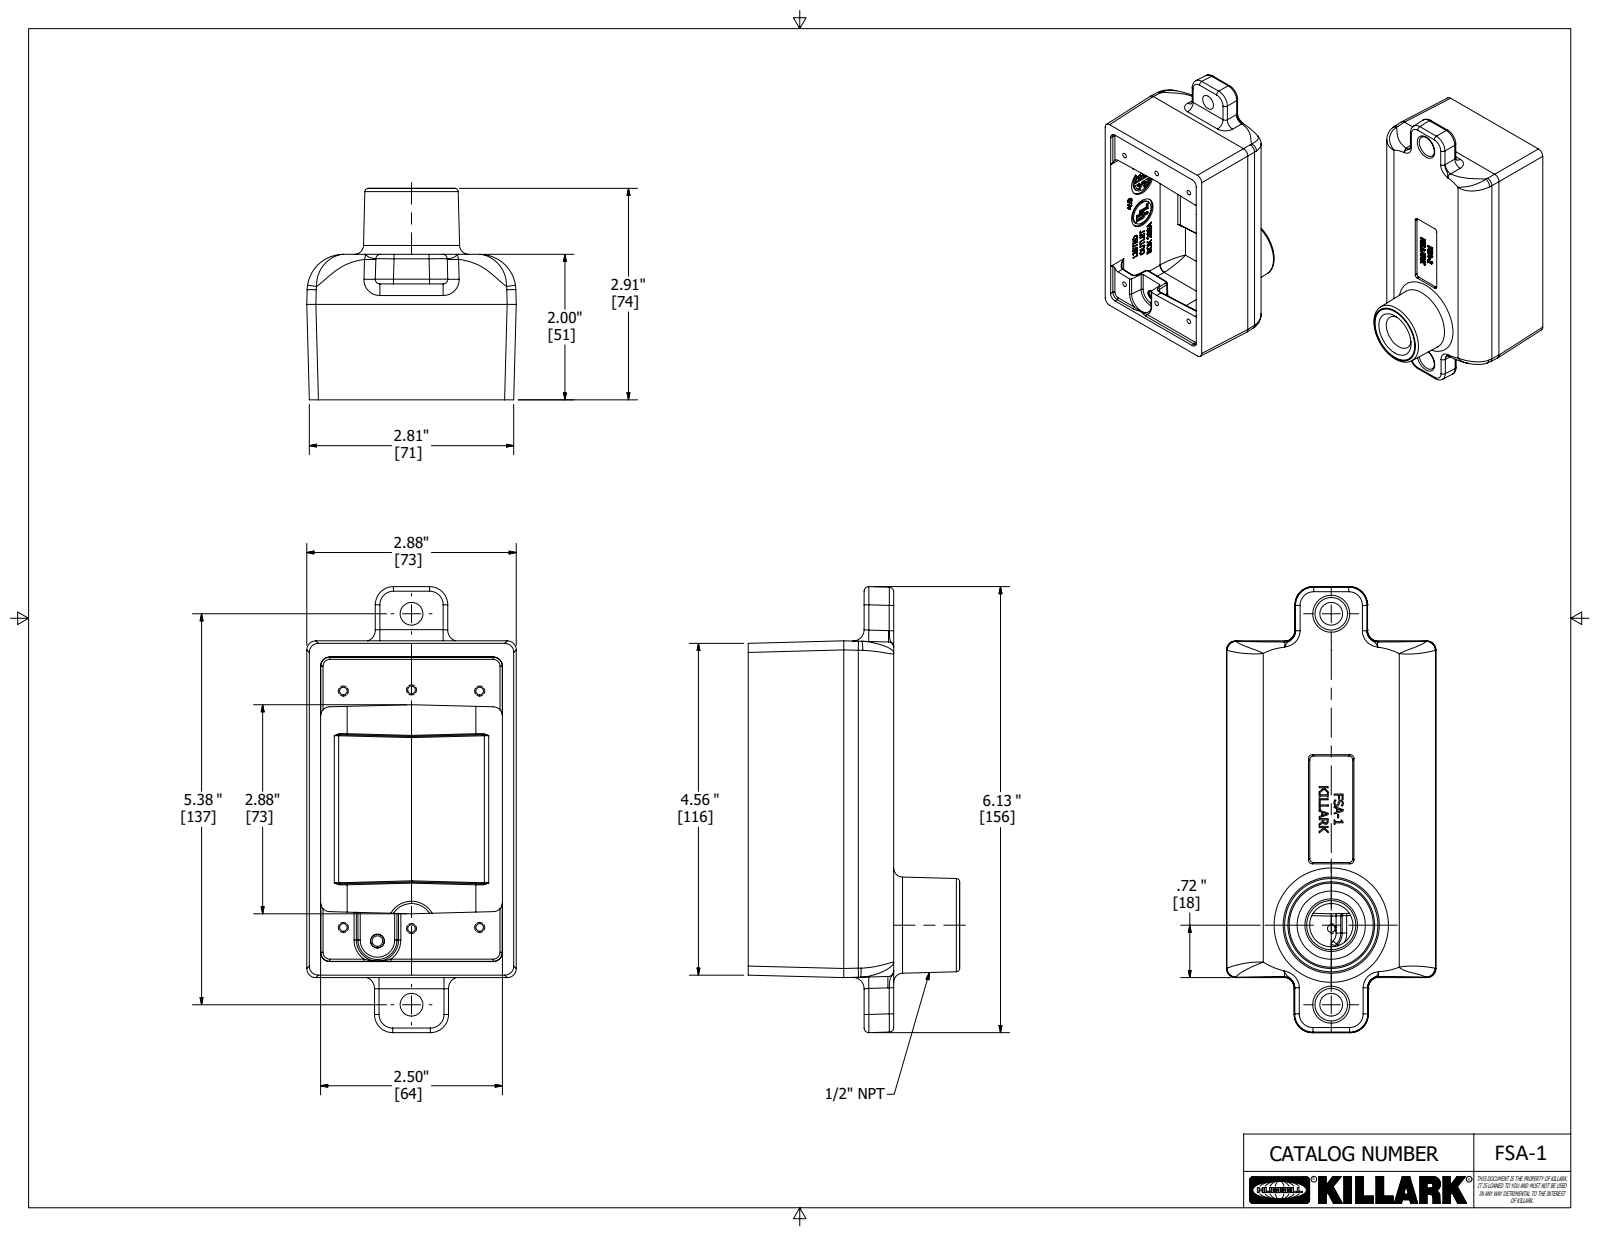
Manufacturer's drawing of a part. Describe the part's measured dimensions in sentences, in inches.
The part is named "24225-2". Its 3-D file was written by "Autodesk Inventor 2020 (AUTOMOTIVE_DESIGN)". It is 1 solid with 1111 faces: 585 planar, 130 cylindrical and 396 other. Overall it measures 6.132 by 2.908 by 2.881 inches. Its volume is 8.961 cubic inches and its surface area 91.74 square inches. Round holes: 6 of diameter 0.104, 1 of diameter 0.069, 1 of diameter 0.145, 1 of diameter 0.595, 1 of diameter 0.625. Round bosses or shafts: 1 of diameter 0.509, 1 of diameter 0.058. Partial cylindrical surfaces (rounded edges, fillets, slot ends): 32 of radius 0.125, 24 of radius 0.062, 16 of radius 0.031, 8 of radius 0.016, 6 of radius 0.156, 6 of radius 0.375, 4 of radius 0.25, 1 of radius 0.007. The main face-to-face distances are 2.5, 0.03, 1.594, 1.906, 0.094, 2, 4.25, 1.564, 2.881, 4.631. The hole center spacings are 0.937, 3.397, 0.938, 1.875, 3.25, 3.352, 3.752, 0.047.
